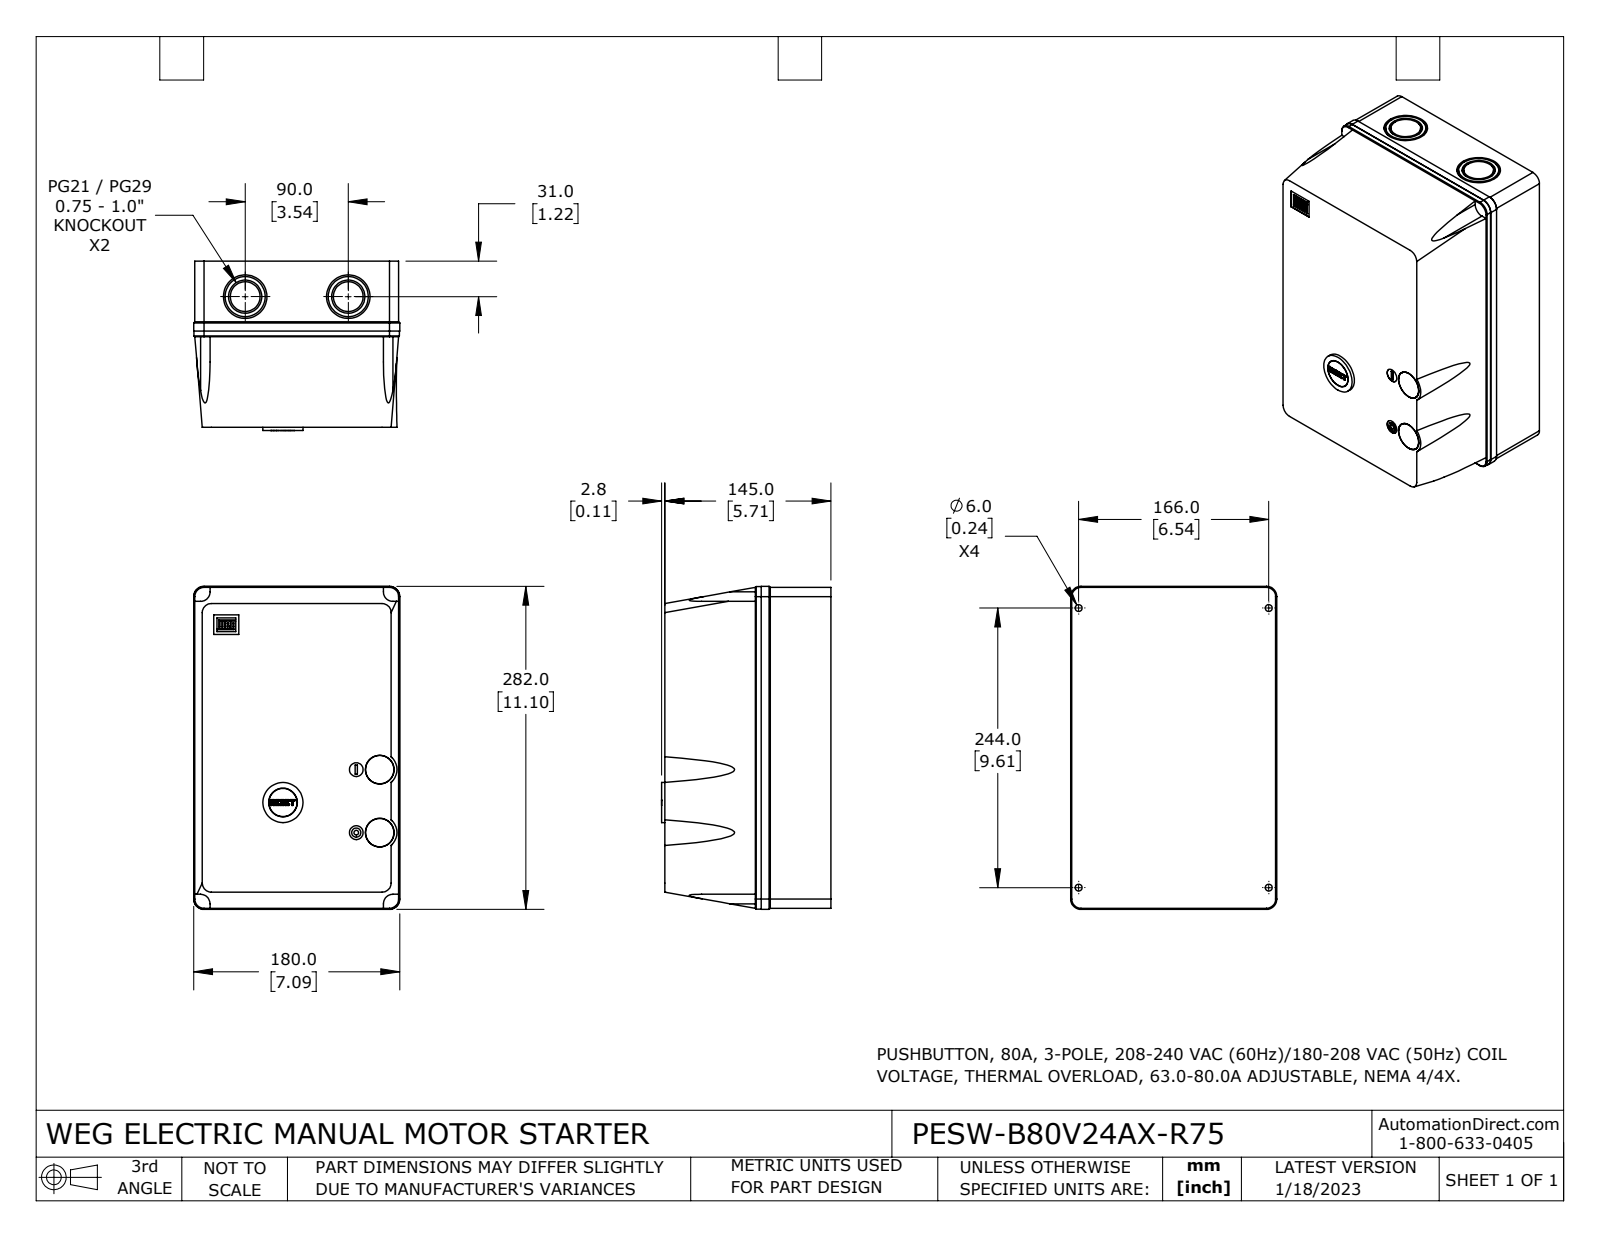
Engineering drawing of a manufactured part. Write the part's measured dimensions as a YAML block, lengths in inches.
part_name: "PESW-B80V24AX-R75"
step_written_by: "SolidWorks 2021 (CONFIG_CONTROL_DESIGN)"
units: inches
bodies: {solids: 3, faces: 286, planar: 130, cylindrical: 144, other: 12}
overall_size: [11.102, 7.087, 5.823]
volume: 428
surface_area: 360
round_holes:
  - {diameter: 0.236, count: 4}
  - {diameter: 0.984, count: 3}
  - {diameter: 0.472, count: 2}
  - {diameter: 1.142, count: 2}
  - {diameter: 1.496, count: 2}
  - {diameter: 0.157, count: 1}
  - {diameter: 1.201, count: 1}
round_bosses_or_shafts:
  - {diameter: 1.378, count: 3}
  - {diameter: 1.024, count: 2}
  - {diameter: 0.976, count: 2}
  - {diameter: 1.193, count: 1}
  - {diameter: 0.969, count: 1}
  - {diameter: 0.551, count: 1}
  - {diameter: 0.315, count: 1}
partial_cylinders:
  - {radius: 0.004, count: 34}
  - {radius: 0.315, count: 4}
  - {radius: 0.327, count: 4}
  - {radius: 0.343, count: 4}
  - {radius: 0.354, count: 4}
  - {radius: 0.063, count: 1}
face_to_face_distances: [5.709, 7.008, 11.024, 0.039, 0.028, 7.047, 7.075, 7.035, 11.063, 7.087]
hole_center_spacings: [0.807, 2.165, 2.311, 6.535, 9.606, 11.619, 1.935, 2.25]
